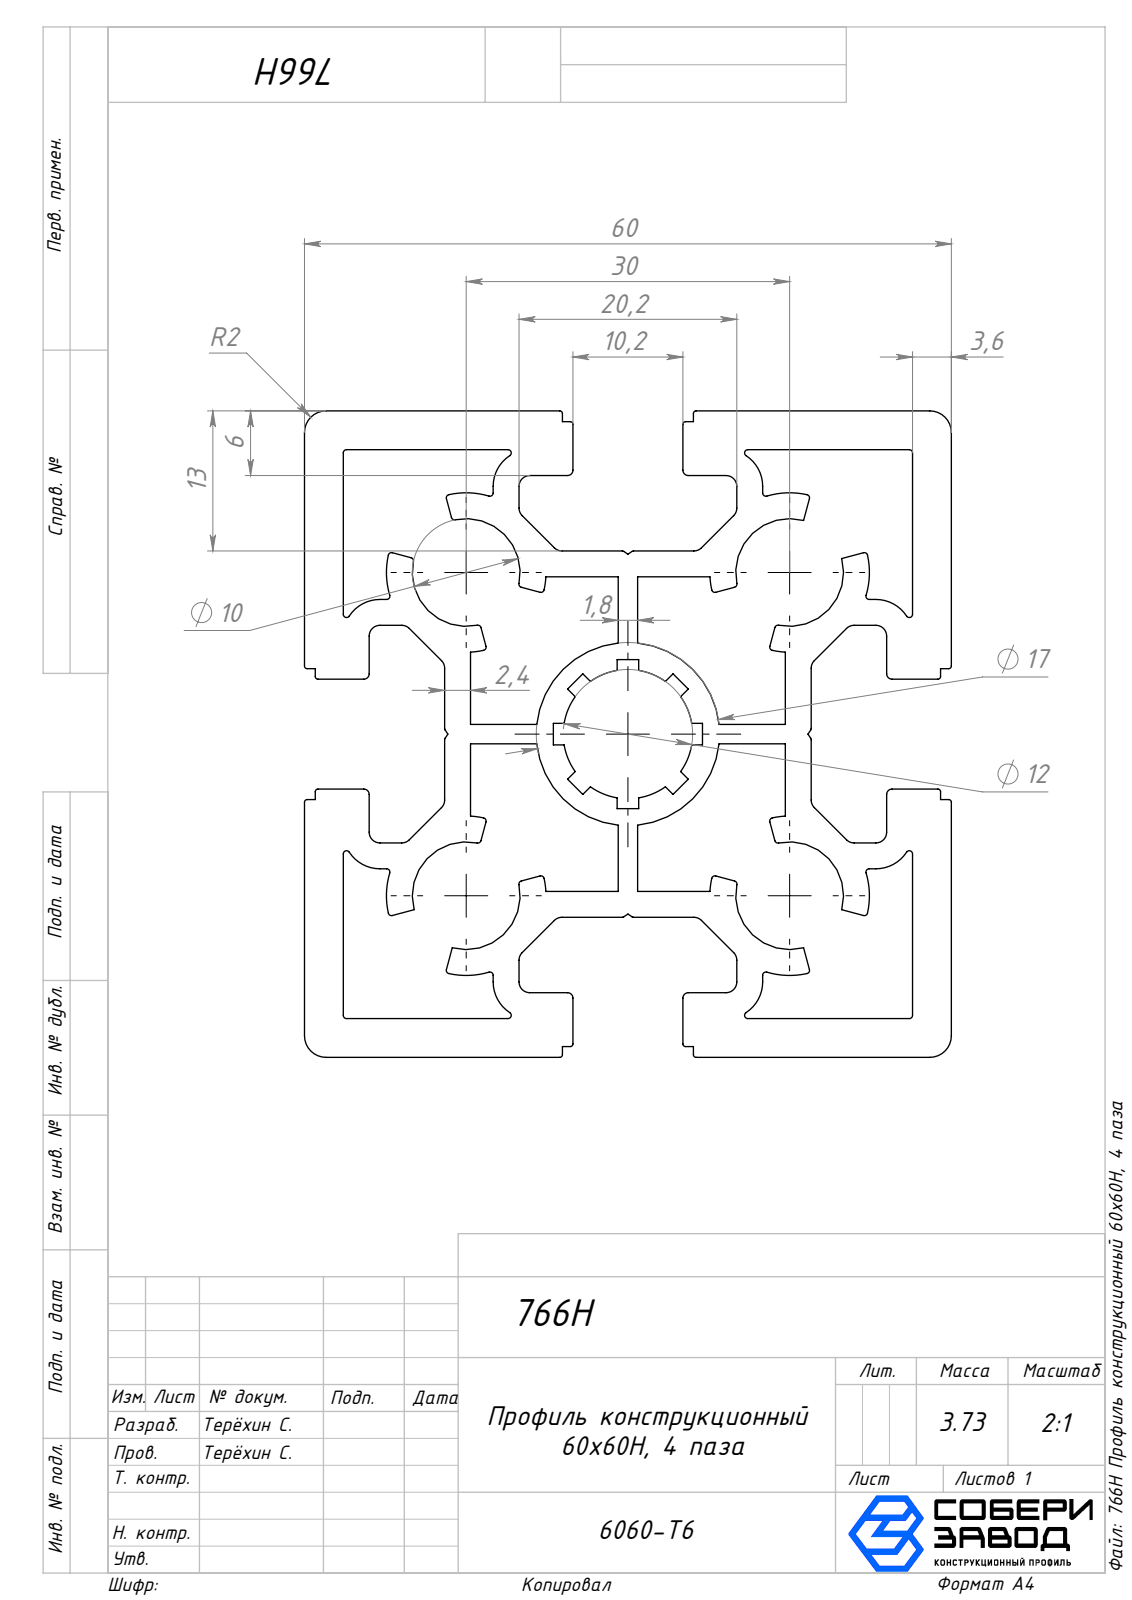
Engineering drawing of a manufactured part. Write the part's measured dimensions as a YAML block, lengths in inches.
part_name: "766H Профиль конструкционный 60х60H, 4 паза_00; Сборка12"
step_written_by: "SolidWorks 2024 (AUTOMOTIVE_DESIGN)"
units: inches
bodies: {solids: 1, faces: 313, planar: 146, cylindrical: 167, other: 0}
overall_size: [39.37, 2.362, 2.362]
volume: 84.33
surface_area: 1442
round_bosses_or_shafts:
  - {diameter: 0.669, count: 1}
partial_cylinders:
  - {radius: 0.012, count: 46}
  - {radius: 0.01, count: 24}
  - {radius: 0.039, count: 24}
  - {radius: 0.02, count: 8}
  - {radius: 0.134, count: 8}
  - {radius: 0.079, count: 4}
  - {radius: 0.197, count: 4}
  - {radius: 0.291, count: 4}
face_to_face_distances: [0.142, 2.22, 2.362, 1.614, 1.146, 0.094, 0.37, 0.236, 0.98, 2.079]
